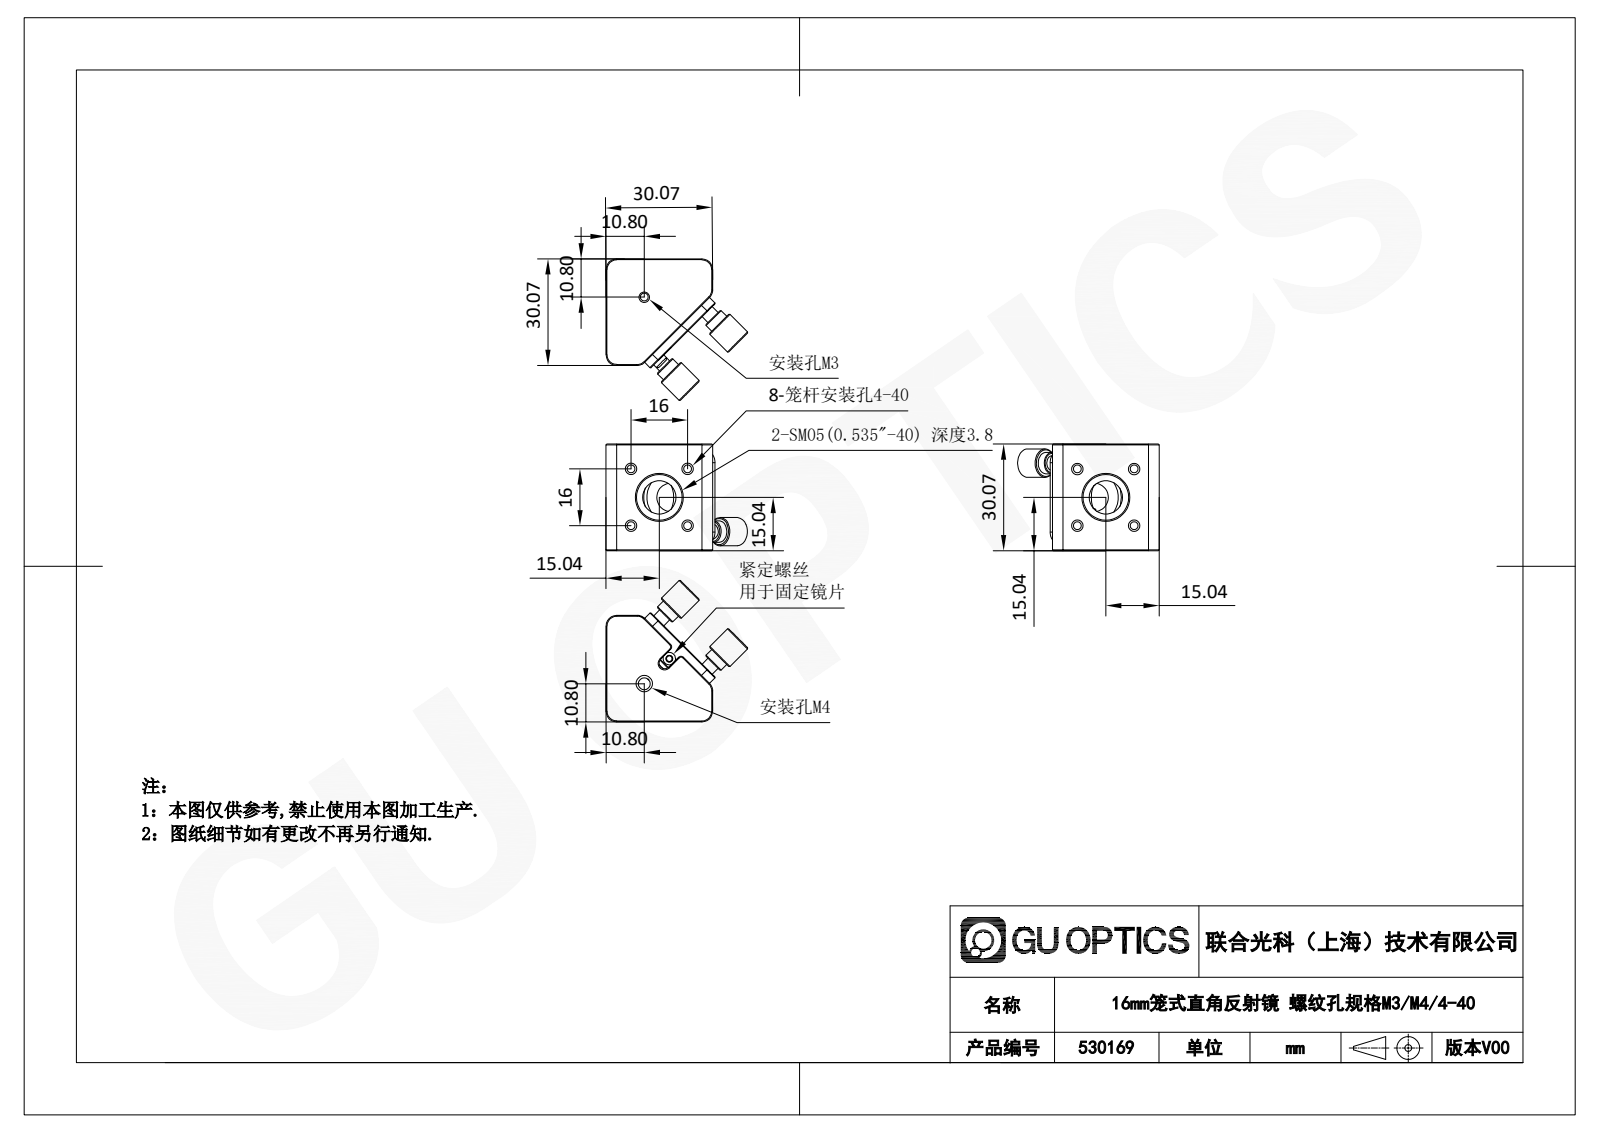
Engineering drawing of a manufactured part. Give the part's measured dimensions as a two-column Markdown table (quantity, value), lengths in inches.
| quantity | value |
| --- | --- |
| part name | 530169 |
| STEP written by | SolidWorks 2020 (CONFIG_CONTROL_DESIGN) |
| units | inches |
| bodies | 16 solids, 367 faces (159 planar, 90 cylindrical, 118 other) |
| overall size | 1.599 × 1.599 × 1.184 |
| volume | 1.016 in³ |
| surface area | 17.4 in² |
| round holes (diameter × count) | 0.089 × 8, 0.138 × 6, 0.148 × 5, 0.114 × 4, 0.118 × 3, 0.098 × 2, 0.374 × 2, 0.51 × 2, 0.549 × 2, 0.13 × 1, 0.181 × 1, 0.47 × 1 |
| round bosses / shafts (diameter × count) | 0.157 × 3, 0.059 × 3, 0.315 × 2, 0.236 × 2, 0.118 × 2, 0.65 × 1, 0.079 × 1 |
| partial cylindrical surfaces (radius × count) | 0.031 × 12, 0.118 × 9, 0.039 × 4, 0.125 × 4, 0.012 × 2, 0.157 × 2, 0.063 × 1, 0.069 × 1 |
| main face-to-face distances | 1.184, 0.03, 1.049, 0.418, 0.118, 0.3, 0.053, 1.131, 1.079, 0.082 |
| hole center spacings | 0.445, 0.63, 0.191, 0.569, 0.891, 0.537, 0.76, 0.783 |
